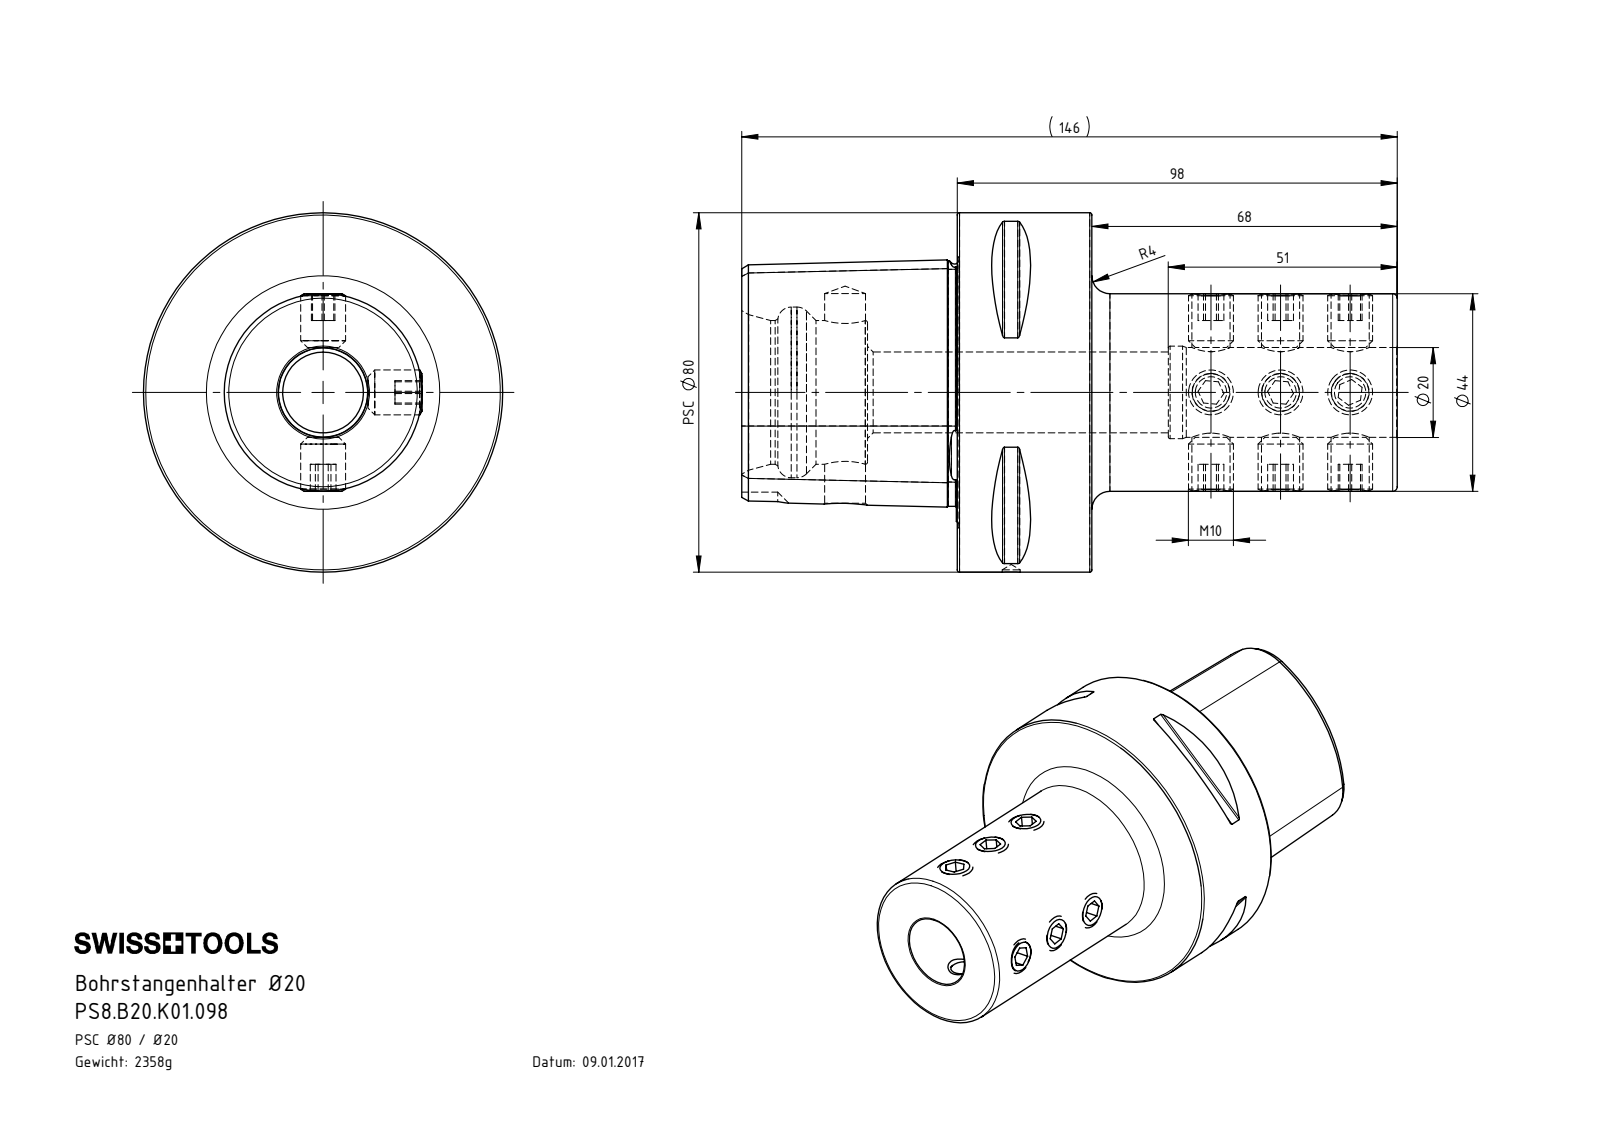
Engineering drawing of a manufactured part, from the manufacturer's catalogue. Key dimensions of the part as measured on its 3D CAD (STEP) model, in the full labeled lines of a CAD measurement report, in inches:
Part name (STEP PRODUCT): PS8.B20.K01.098; ISO 4026 - M10 x 12_PreviewCfg; PS8-B20.K01.098_A
STEP written by: SolidWorks 2015 (AUTOMOTIVE_DESIGN)
Units: inches
Bodies: 10 solids, 292 faces (102 planar, 67 cylindrical, 123 other)
Overall size (bounding box): 5.748 × 3.15 × 3.15
Volume: 18.33 in³ · Surface area: 80.73 in²
Round holes (diameter × count): ⌀0.335 ×6, ⌀0.157 ×1, ⌀0.358 ×1, ⌀0.709 ×1, ⌀0.787 ×1, ⌀0.811 ×1, ⌀1.26 ×1, ⌀1.496 ×1
Round bosses / shafts (diameter × count): ⌀0.394 ×6, ⌀3.15 ×1, ⌀1.732 ×1
Partial cylindrical surfaces — rounded edges, fillets, slot ends (radius × count): R0.02 ×8, R0.236 ×1
Main face-to-face distances: 1.181, 3.858, 2.677, 1.89, 3.071, 5.748, 0.787, 1.281, 1.102, 1.969
Hole centre spacings: 0.61, 1.22, 1.457, 1.752, 2.362, 2.972, 3.209, 3.819
